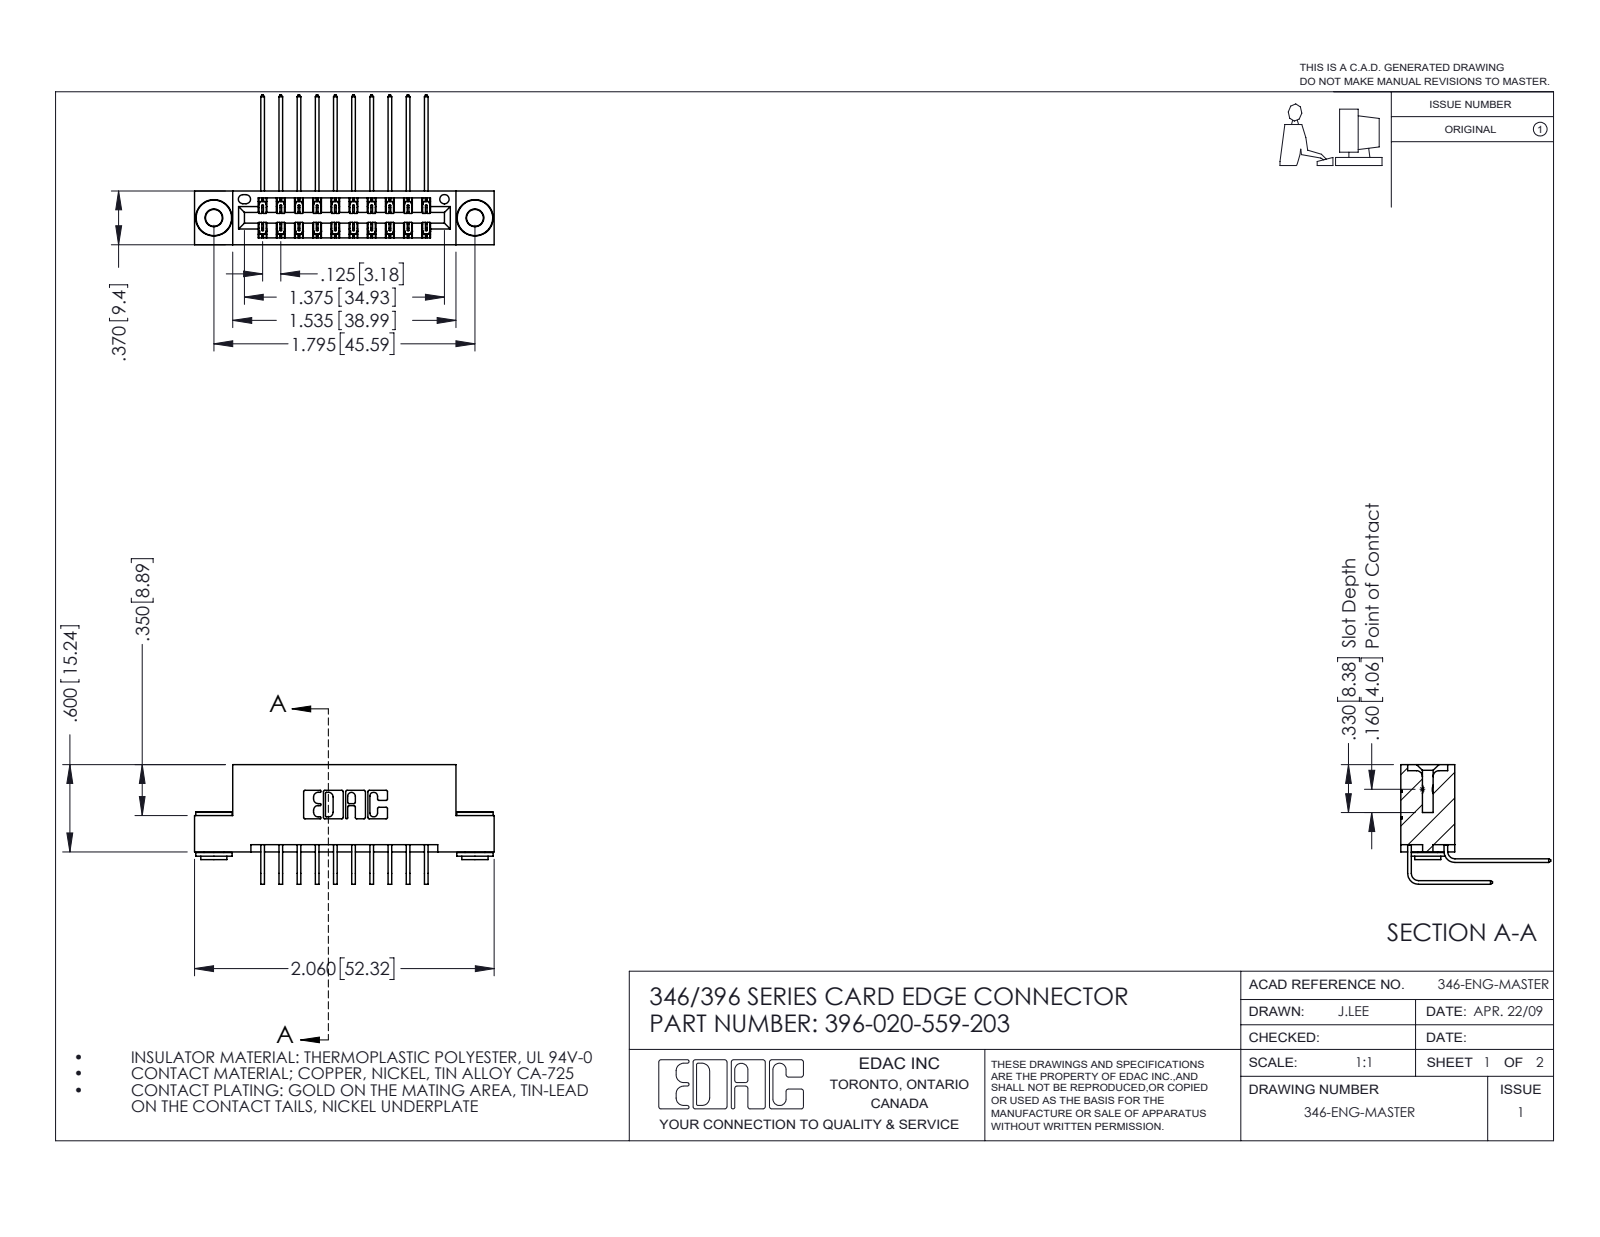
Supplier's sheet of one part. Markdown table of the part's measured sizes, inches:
| quantity | value |
| --- | --- |
| part name | 345-250-002_345-250-002-102; 346 Part_Flush Mounting Lugs - 0.156 Dia-TH; 345-292-001_558 559 Tail - 1; 396-020-559-203 (+1 more) |
| STEP written by | SolidWorks 2016 (CONFIG_CONTROL_DESIGN) |
| units | inches |
| bodies | 23 solids, 1240 faces (826 planar, 406 cylindrical, 8 other) |
| overall size | 2.06 × 1.03 × 0.823 |
| volume | 0.304 in³ |
| surface area | 11.04 in² |
| round holes (diameter × count) | 0.116 × 2, 0.156 × 2, 0.064 × 1 |
| round bosses / shafts (diameter × count) | 0.25 × 2, 0.18 × 2, 0.136 × 2 |
| partial cylindrical surfaces (radius × count) | 0.006 × 30, 0.01 × 22, 0.007 × 6, 0.031 × 6, 0.026 × 3, 0.014 × 2, 0.022 × 2, 0.024 × 2 |
| main face-to-face distances | 0.25, 0.048, 0.322, 0.37, 0.025, 0.298, 0.072, 0.275, 0.148, 0.222 |
| hole center spacings | 0.246, 1.59, 1.795 |
